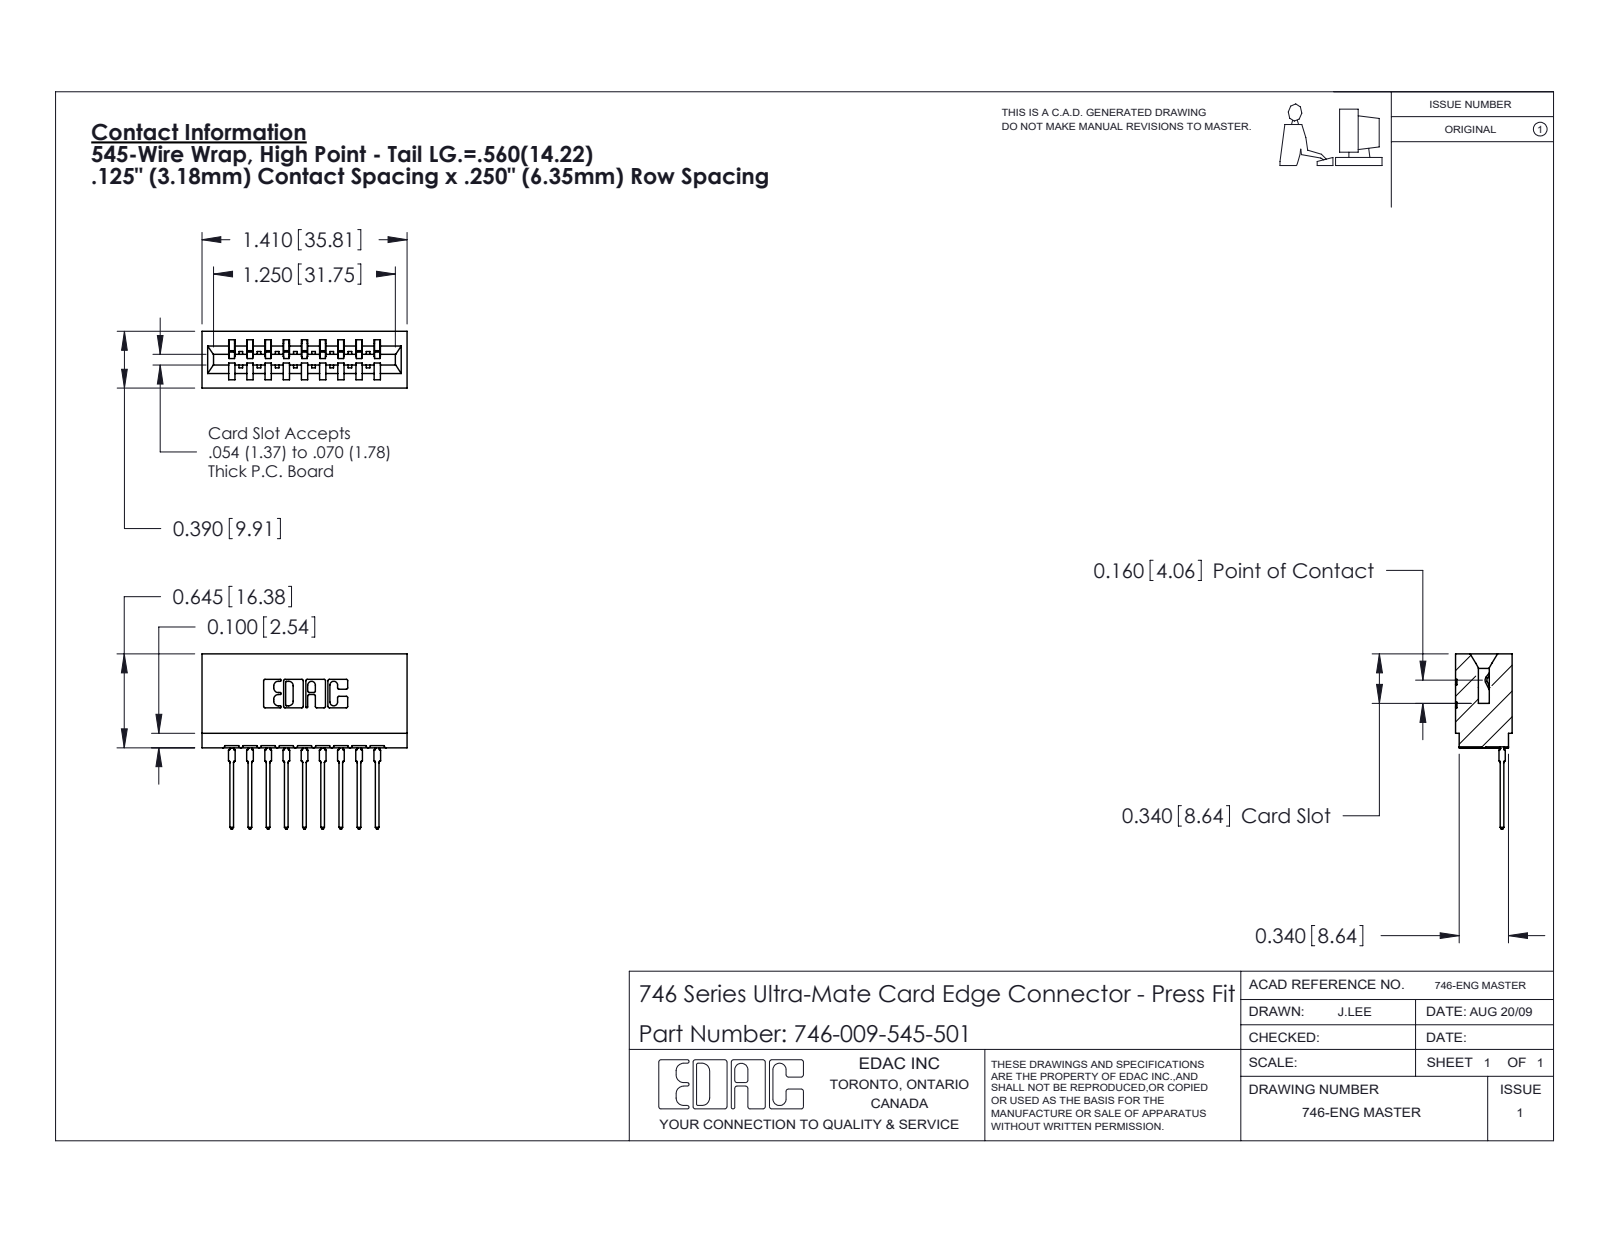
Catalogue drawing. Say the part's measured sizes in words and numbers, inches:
The part is named "746 Part_.340 Slot Depth - 01; 746-292-001_545; 746-009-545-501". Its 3-D file was written by "SolidWorks 2020 (CONFIG_CONTROL_DESIGN)". It is 10 solids with 1069 faces: 622 planar, 213 cylindrical and 234 other. Overall it measures 1.41 by 1.204 by 0.39 inches. Its volume is 0.259 cubic inches and its surface area 8.297 square inches. Partial cylindrical surfaces (rounded edges, fillets, slot ends): 22 of radius 0.01, 18 of radius 0.021, 10 of radius 0.015, 6 of radius 0.007, 6 of radius 0.031, 4 of radius 0.005, 4 of radius 0.011, 3 of radius 0.026. The main face-to-face distances are 0.25, 0.5, 0.042, 0.333, 0.125, 0.125, 0.057, 0.292, 0.208, 0.375.
